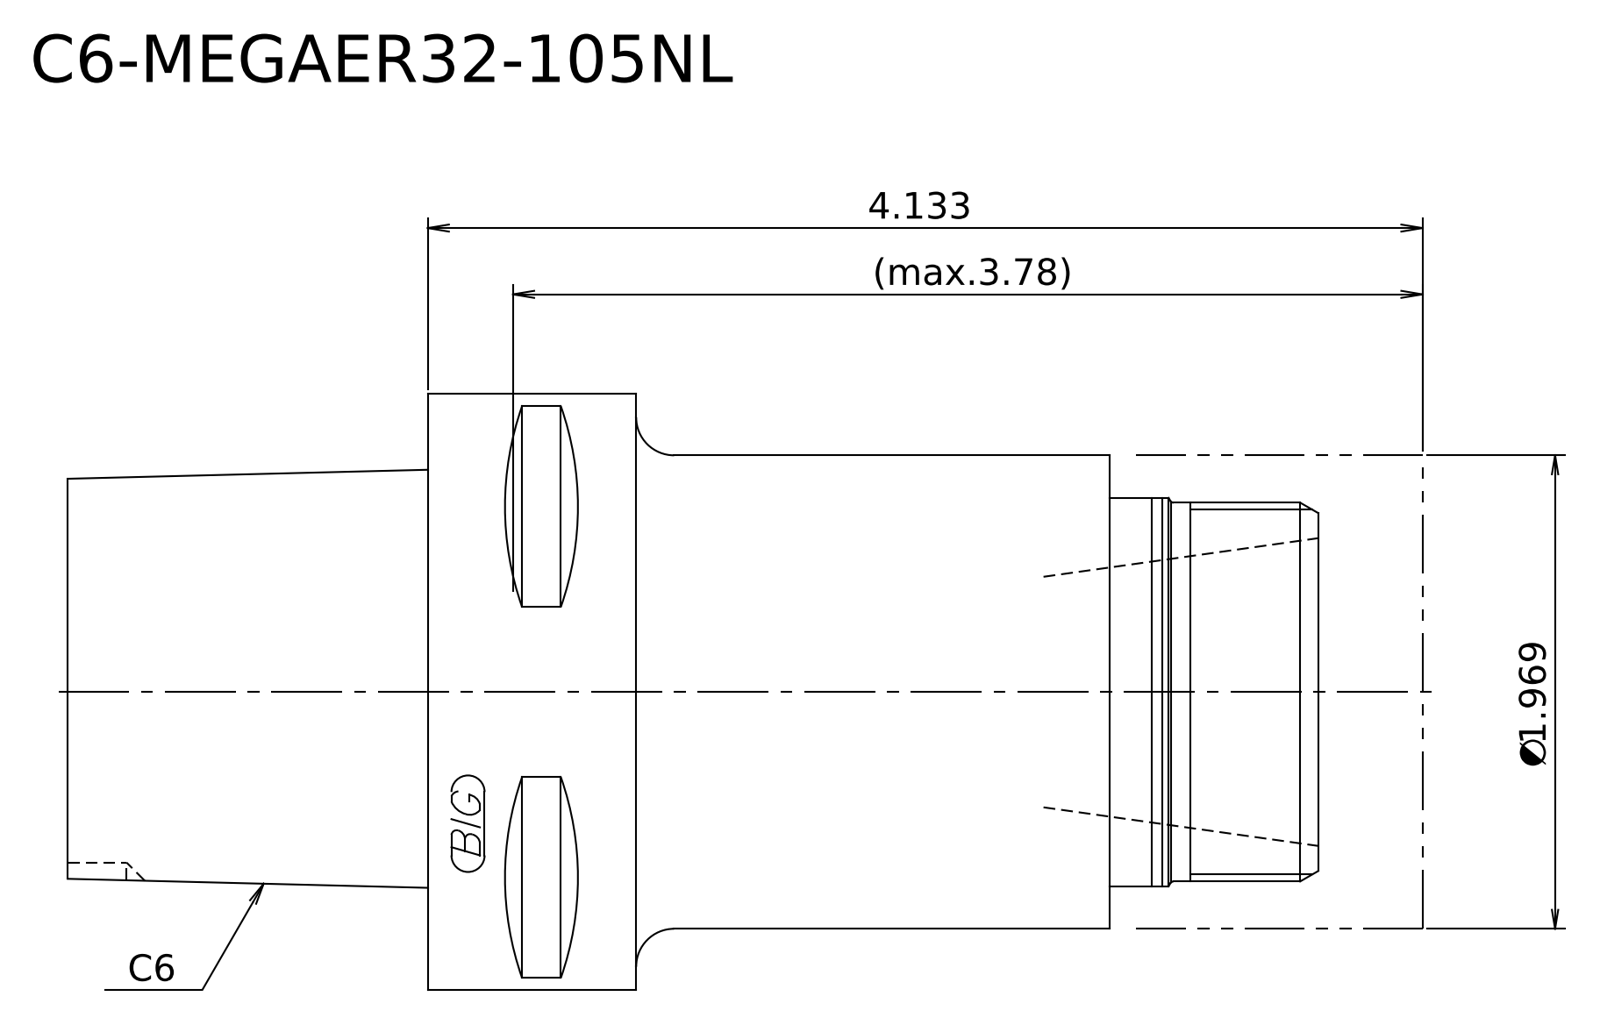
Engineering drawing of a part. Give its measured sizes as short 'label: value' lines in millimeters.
written by: Kubotek KeyCreator 2011 V10.0.2 (22737) (automotive_design)
unit: mm
bodies: 2 solids, 18 faces (7 planar, 5 cylindrical, 6 other)
size: 143 × 63 × 63
volume: 310 086 mm³; area: 34 448 mm²
bosses: 1× ⌀63, 1× ⌀50, 1× ⌀41, 1× ⌀40
face distances: 30.2, 105, 74.8, 143, 112.8, 38, 11, 19.2, 94, 132
